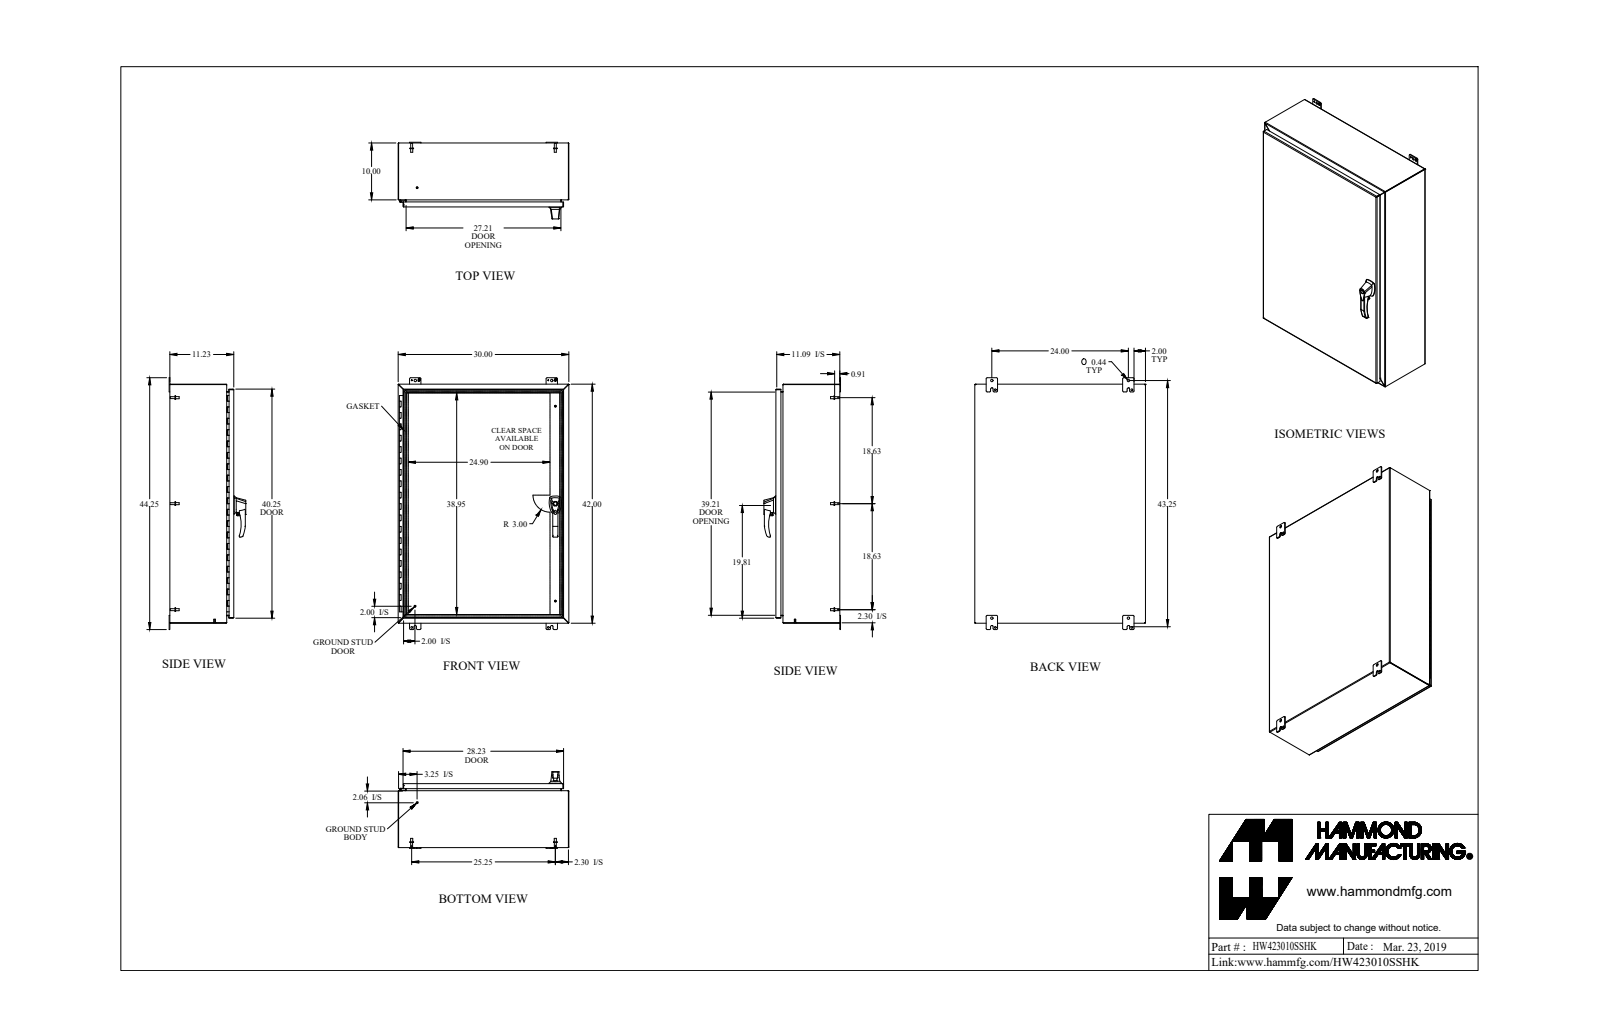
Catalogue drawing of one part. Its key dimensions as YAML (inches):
part_name: "HW423010SSHK"
step_written_by: "SolidWorks 2018 (AUTOMOTIVE_DESIGN)"
units: inches
bodies: {solids: 44, faces: 1599, planar: 761, cylindrical: 671, other: 167}
overall_size: [44.25, 30, 13.473]
volume: 380.5
surface_area: 9346
round_holes:
  - {diameter: 0.176, count: 6}
  - {diameter: 0.313, count: 5}
  - {diameter: 0.25, count: 3}
  - {diameter: 0.265, count: 3}
  - {diameter: 0.413, count: 3}
  - {diameter: 0.196, count: 2}
  - {diameter: 0.256, count: 2}
  - {diameter: 0.394, count: 2}
  - {diameter: 0.437, count: 2}
  - {diameter: 0.187, count: 1}
  - {diameter: 0.233, count: 1}
  - {diameter: 0.33, count: 1}
round_bosses_or_shafts:
  - {diameter: 0.375, count: 11}
  - {diameter: 0.25, count: 7}
  - {diameter: 0.65, count: 6}
  - {diameter: 0.332, count: 6}
  - {diameter: 0.156, count: 6}
  - {diameter: 1, count: 3}
  - {diameter: 0.51, count: 3}
  - {diameter: 0.63, count: 2}
partial_cylinders:
  - {radius: 0.25, count: 27}
  - {radius: 0.188, count: 22}
  - {radius: 0.036, count: 16}
  - {radius: 0.108, count: 16}
  - {radius: 0.06, count: 12}
  - {radius: 0.125, count: 9}
  - {radius: 0.045, count: 8}
  - {radius: 0.218, count: 8}
face_to_face_distances: [0.072, 11.138, 11.066, 0.095, 11.233, 11.161, 29.928, 41.928, 29.856, 30]
hole_center_spacings: [1.111, 17.118, 17.119, 34.237, 4.195, 17.119, 24, 24.724]
